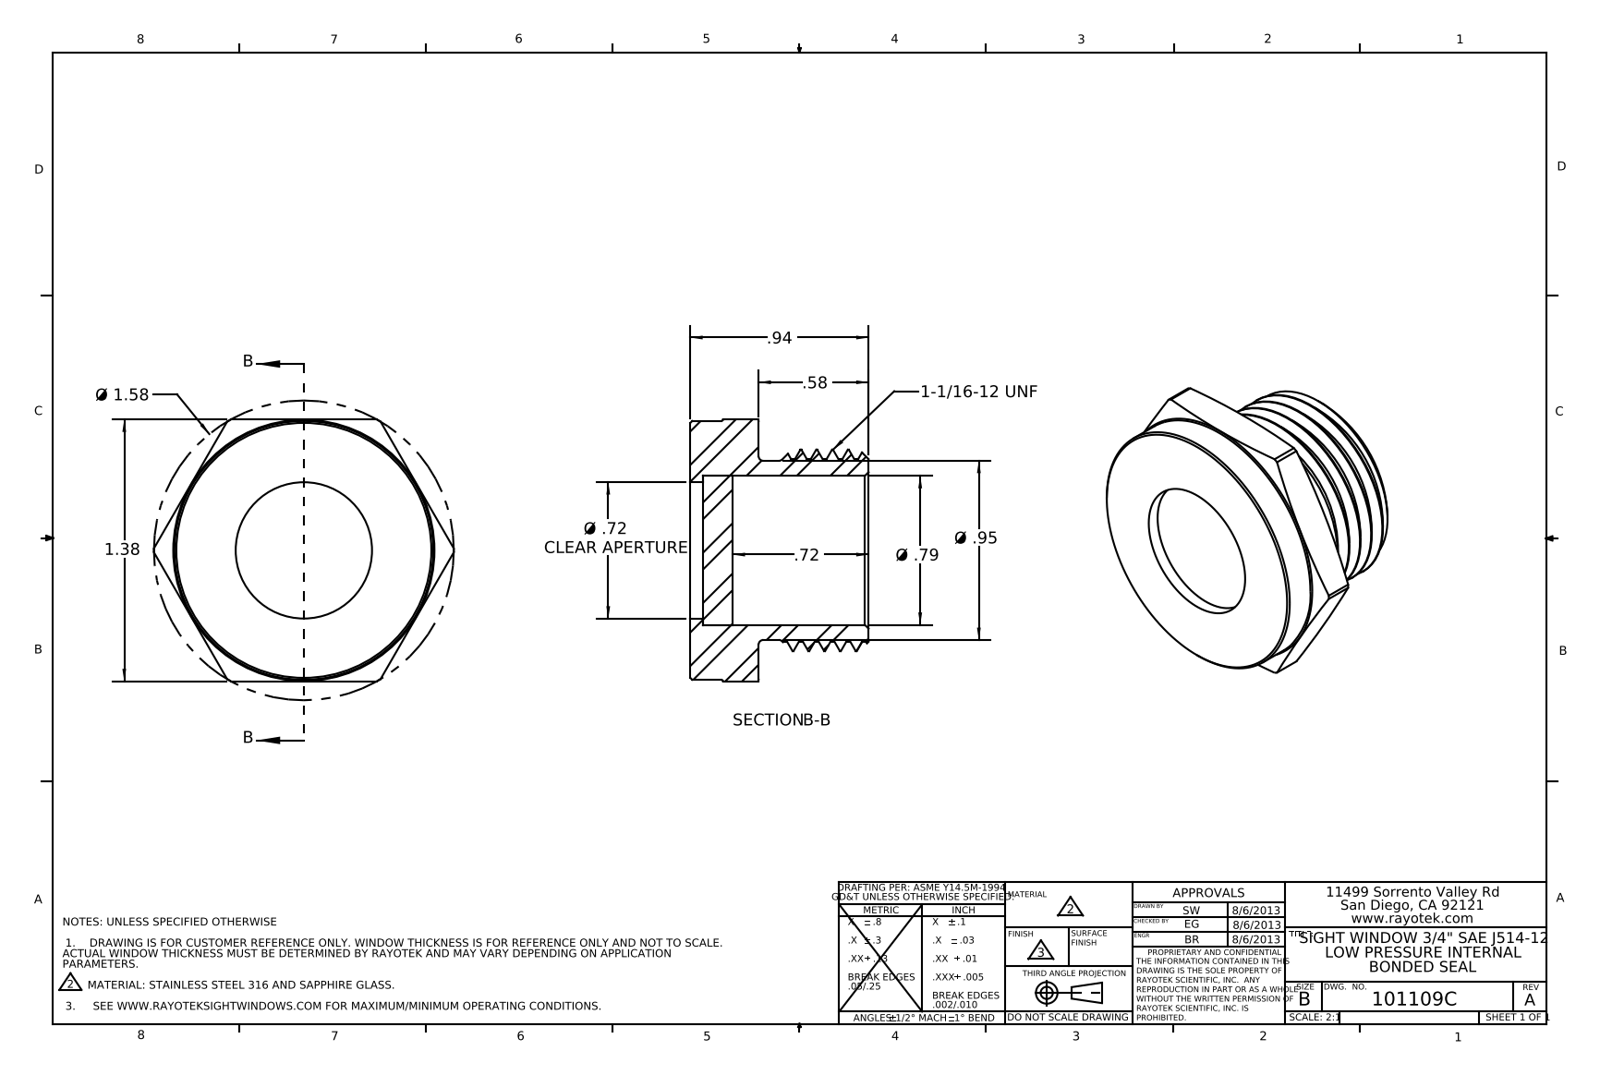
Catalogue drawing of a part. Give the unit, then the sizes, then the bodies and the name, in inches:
Units: inches
Overall size (bounding box): 1.581 × 1.38 × 0.94
Round holes (diameter × count): ⌀0.719 ×1, ⌀0.785 ×1
Round bosses / shafts (diameter × count): ⌀1.365 ×1, ⌀1.063 ×1, ⌀0.945 ×1
Partial cylindrical surfaces — rounded edges, fillets, slot ends (radius × count): R0.791 ×1
Main face-to-face distances: 0.36, 0.294, 0.066, 0.137, 0.157, 0.223, 1.38, 0.58, 0.717, 0.874
Volume: 0.631 in³ · Surface area: 10.38 in²
Bodies: 2 solids, 61 faces (12 planar, 26 cylindrical, 23 other)
Part name (STEP PRODUCT): 403109
STEP written by: SolidWorks 2012 (AUTOMOTIVE_DESIGN)
